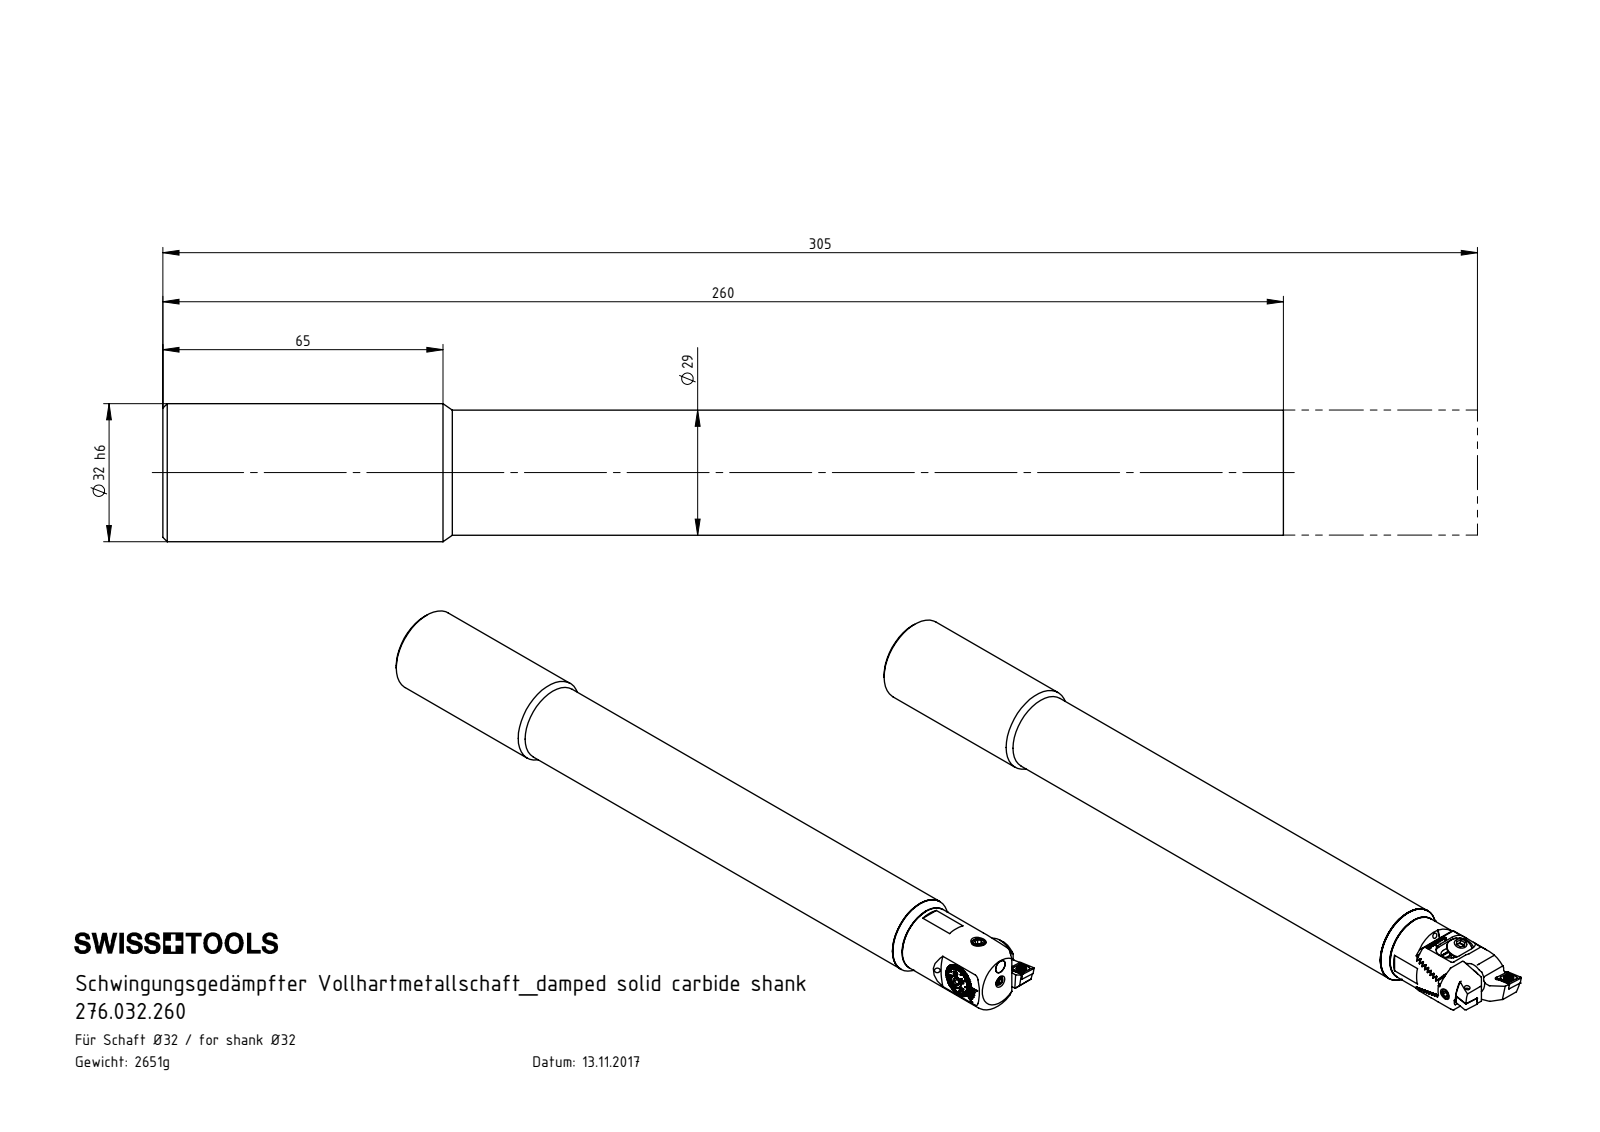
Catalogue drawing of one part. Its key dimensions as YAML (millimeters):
part_name: "HP5-ER2.012.030_A; F25-BG3.005.018_A_Abgedreht; F25-WCA.001.006; ISO 4026 - M5 x 4_PreviewCfg (+8 more)"
step_written_by: "SolidWorks 2017 (CONFIG_CONTROL_DESIGN)"
units: millimeters
bodies: {solids: 22, faces: 878, planar: 372, cylindrical: 172, other: 334}
overall_size: [305, 32, 32]
volume: 195471
surface_area: 49652
round_holes:
  - {diameter: 2, count: 5}
  - {diameter: 4.2, count: 3}
  - {diameter: 2.05, count: 2}
  - {diameter: 2.1, count: 1}
  - {diameter: 2.4, count: 1}
  - {diameter: 2.7, count: 1}
  - {diameter: 2.8, count: 1}
  - {diameter: 3, count: 1}
  - {diameter: 3.3, count: 1}
  - {diameter: 3.85, count: 1}
  - {diameter: 5, count: 1}
  - {diameter: 5.5, count: 1}
round_bosses_or_shafts:
  - {diameter: 5, count: 2}
  - {diameter: 4.95, count: 2}
  - {diameter: 2.5, count: 2}
  - {diameter: 32, count: 1}
  - {diameter: 29, count: 1}
  - {diameter: 25, count: 1}
  - {diameter: 16, count: 1}
  - {diameter: 12.98, count: 1}
partial_cylinders:
  - {radius: 0.21, count: 6}
  - {radius: 0.36, count: 5}
  - {radius: 0.5, count: 4}
  - {radius: 1.32, count: 2}
  - {radius: 0.2, count: 1}
  - {radius: 0.36, count: 1}
  - {radius: 1.05, count: 1}
  - {radius: 1.25, count: 1}
face_to_face_distances: [260, 3, 224, 36, 263, 39, 302.15, 78.15, 42.15, 39.15]
hole_center_spacings: [3.84, 3.99, 4.48, 6.8, 9.46, 16.65]
